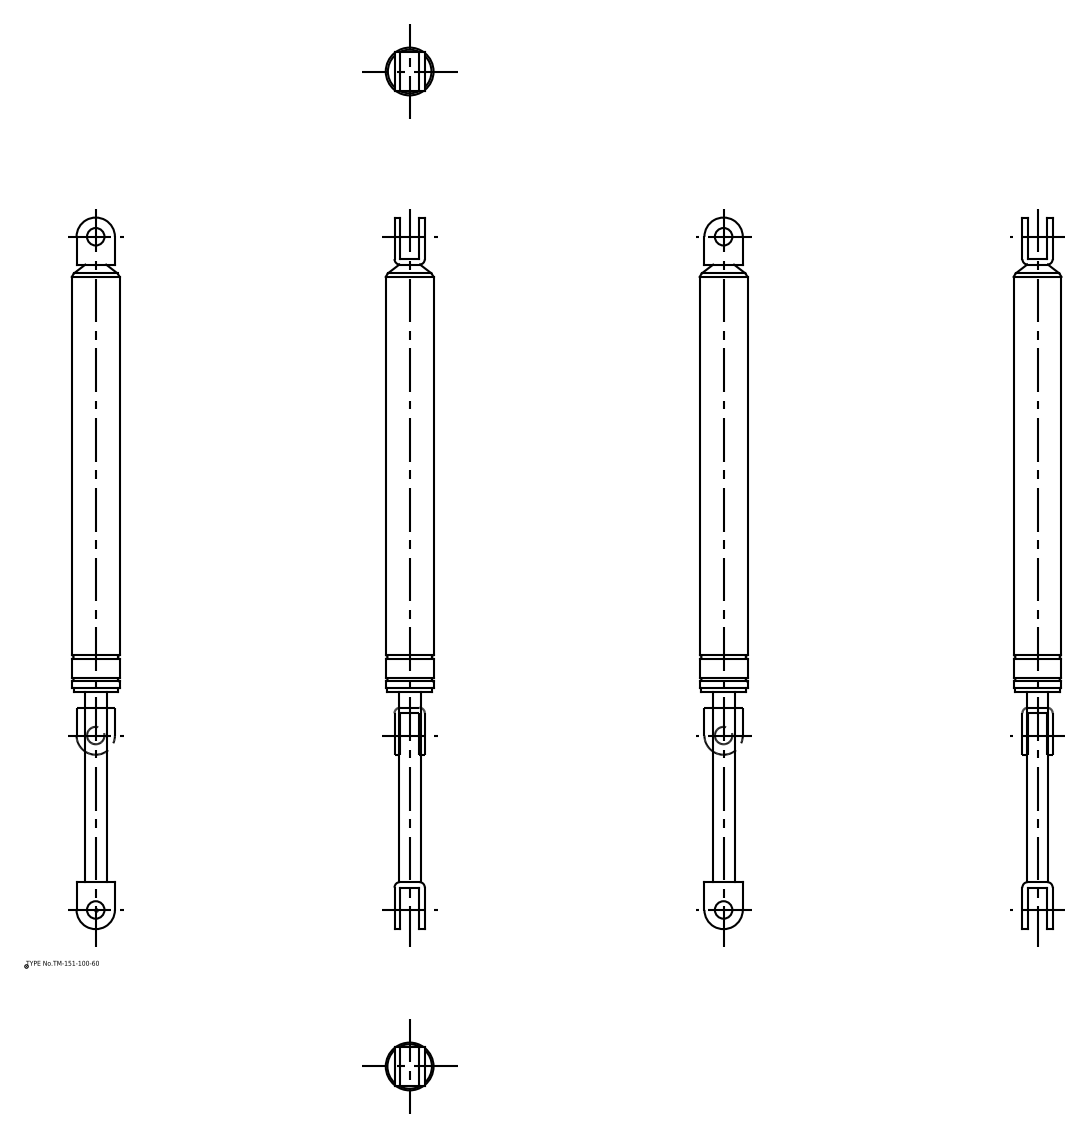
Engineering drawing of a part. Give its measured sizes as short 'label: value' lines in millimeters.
name: TM_151_100_60; TM_151_100_60_div
written by: spGate 16.7.1 (AUTOMOTIVE_DESIGN)
unit: mm
bodies: 2 solids, 64 faces (22 planar, 32 cylindrical, 10 other)
size: 408 × 28.2 × 28.2
volume: 163 537 mm³; area: 32 152 mm²
holes: 2× ⌀10
bosses: 1× ⌀28.2, 1× ⌀27.4, 1× ⌀25.5, 1× ⌀12.5
rounds: 4× R3.2, 2× R11
face distances: 3.2, 14.2, 17.4, 11, 22, 357.2, 112.2, 360.4, 248.2, 245
hole spacings: 386
